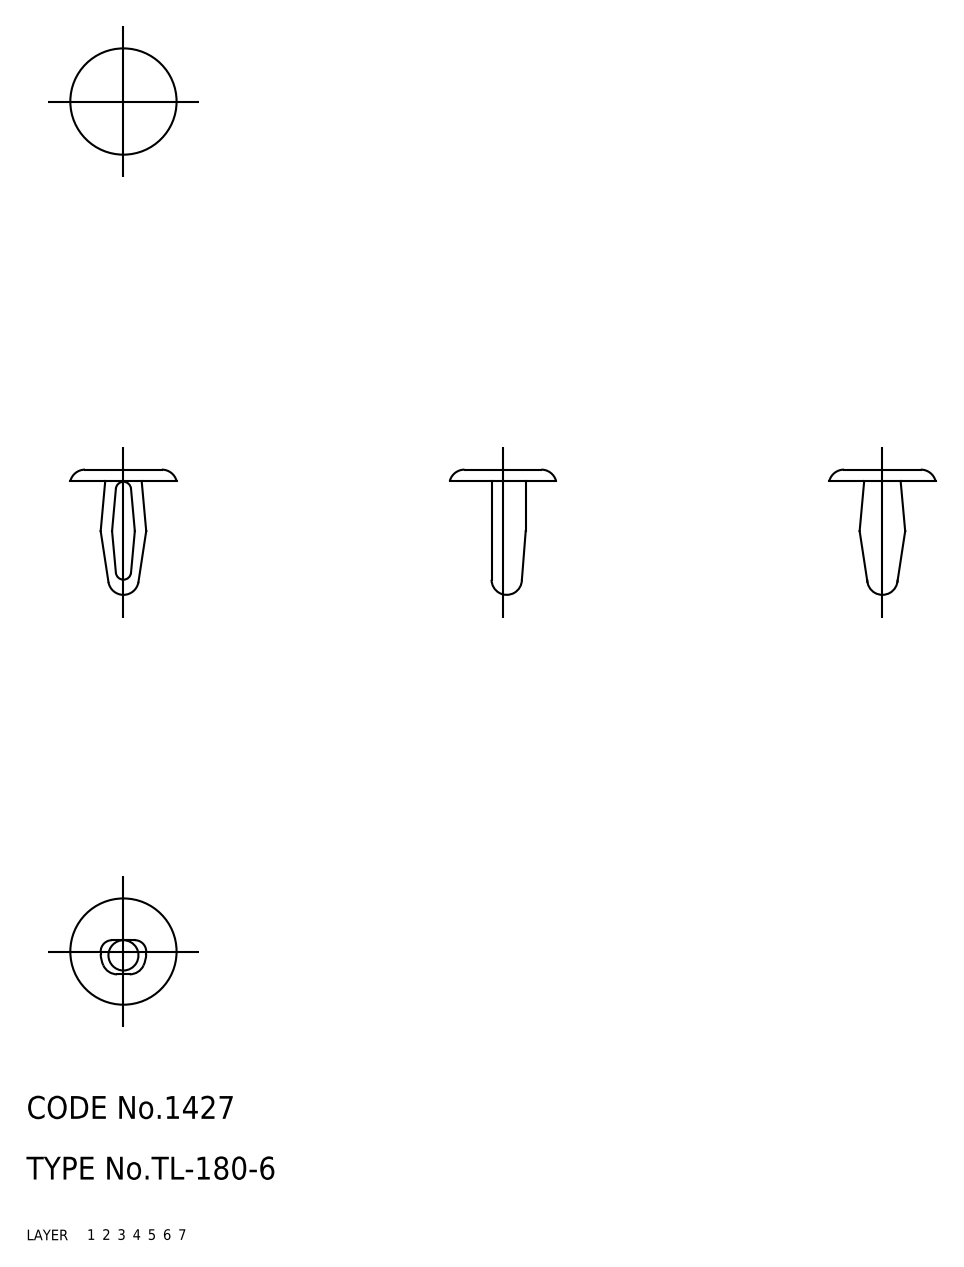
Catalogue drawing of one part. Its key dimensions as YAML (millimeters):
part_name: "fastener"
step_written_by: "CADfix (AUTOMOTIVE_DESIGN)"
units: millimeters
bodies: {solids: 1, faces: 34, planar: 0, cylindrical: 0, other: 34}
overall_size: [16.5, 14, 14]
volume: 408
surface_area: 618
